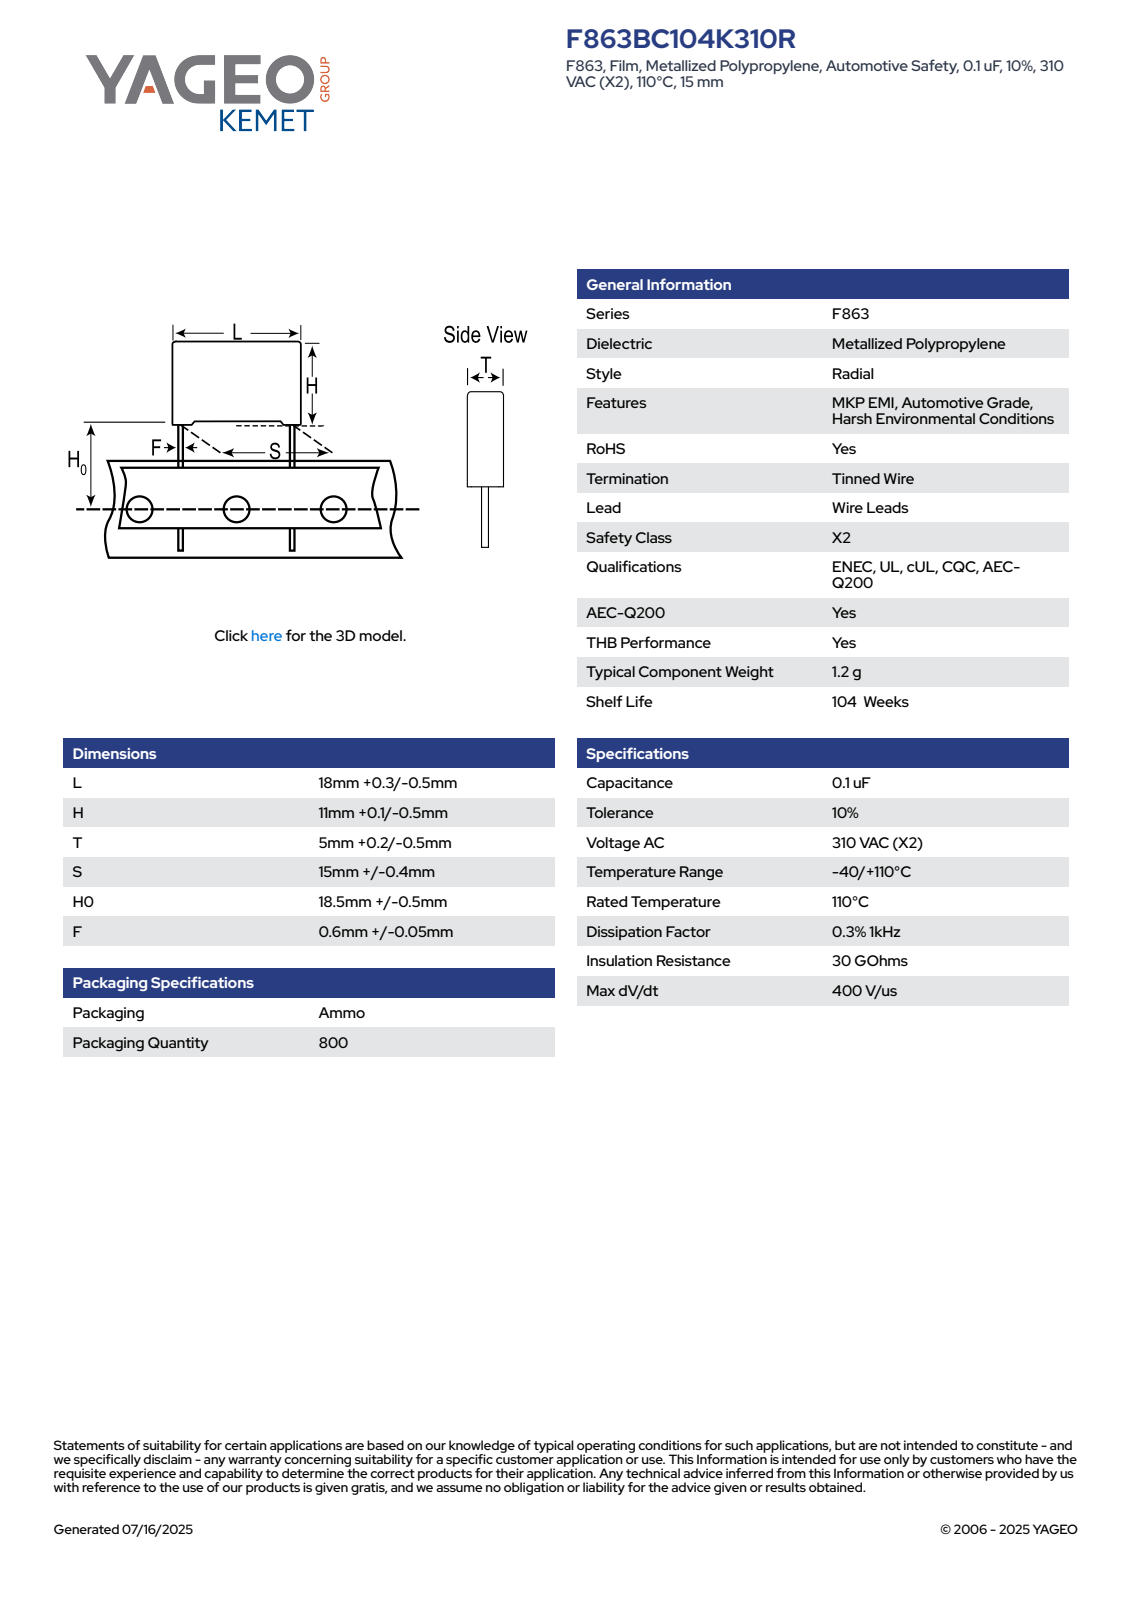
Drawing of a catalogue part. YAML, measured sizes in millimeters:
part_name: "CFR_RB_18X11X5_L18.3H11.1T5.2S15LL19F0.65"
step_written_by: "SolidWorks 2014 (AUTOMOTIVE_DESIGN)"
units: millimeters
bodies: {solids: 4, faces: 89, planar: 81, cylindrical: 8, other: 0}
overall_size: [30.1, 18.3, 5.21]
volume: 1023
surface_area: 796
round_bosses_or_shafts:
  - {diameter: 0.65, count: 2}
partial_cylinders:
  - {radius: 0.4, count: 4}
face_to_face_distances: [5.2, 10.6, 18.3, 0.5, 11.1, 0.6, 4.6, 4, 8.74, 19]
